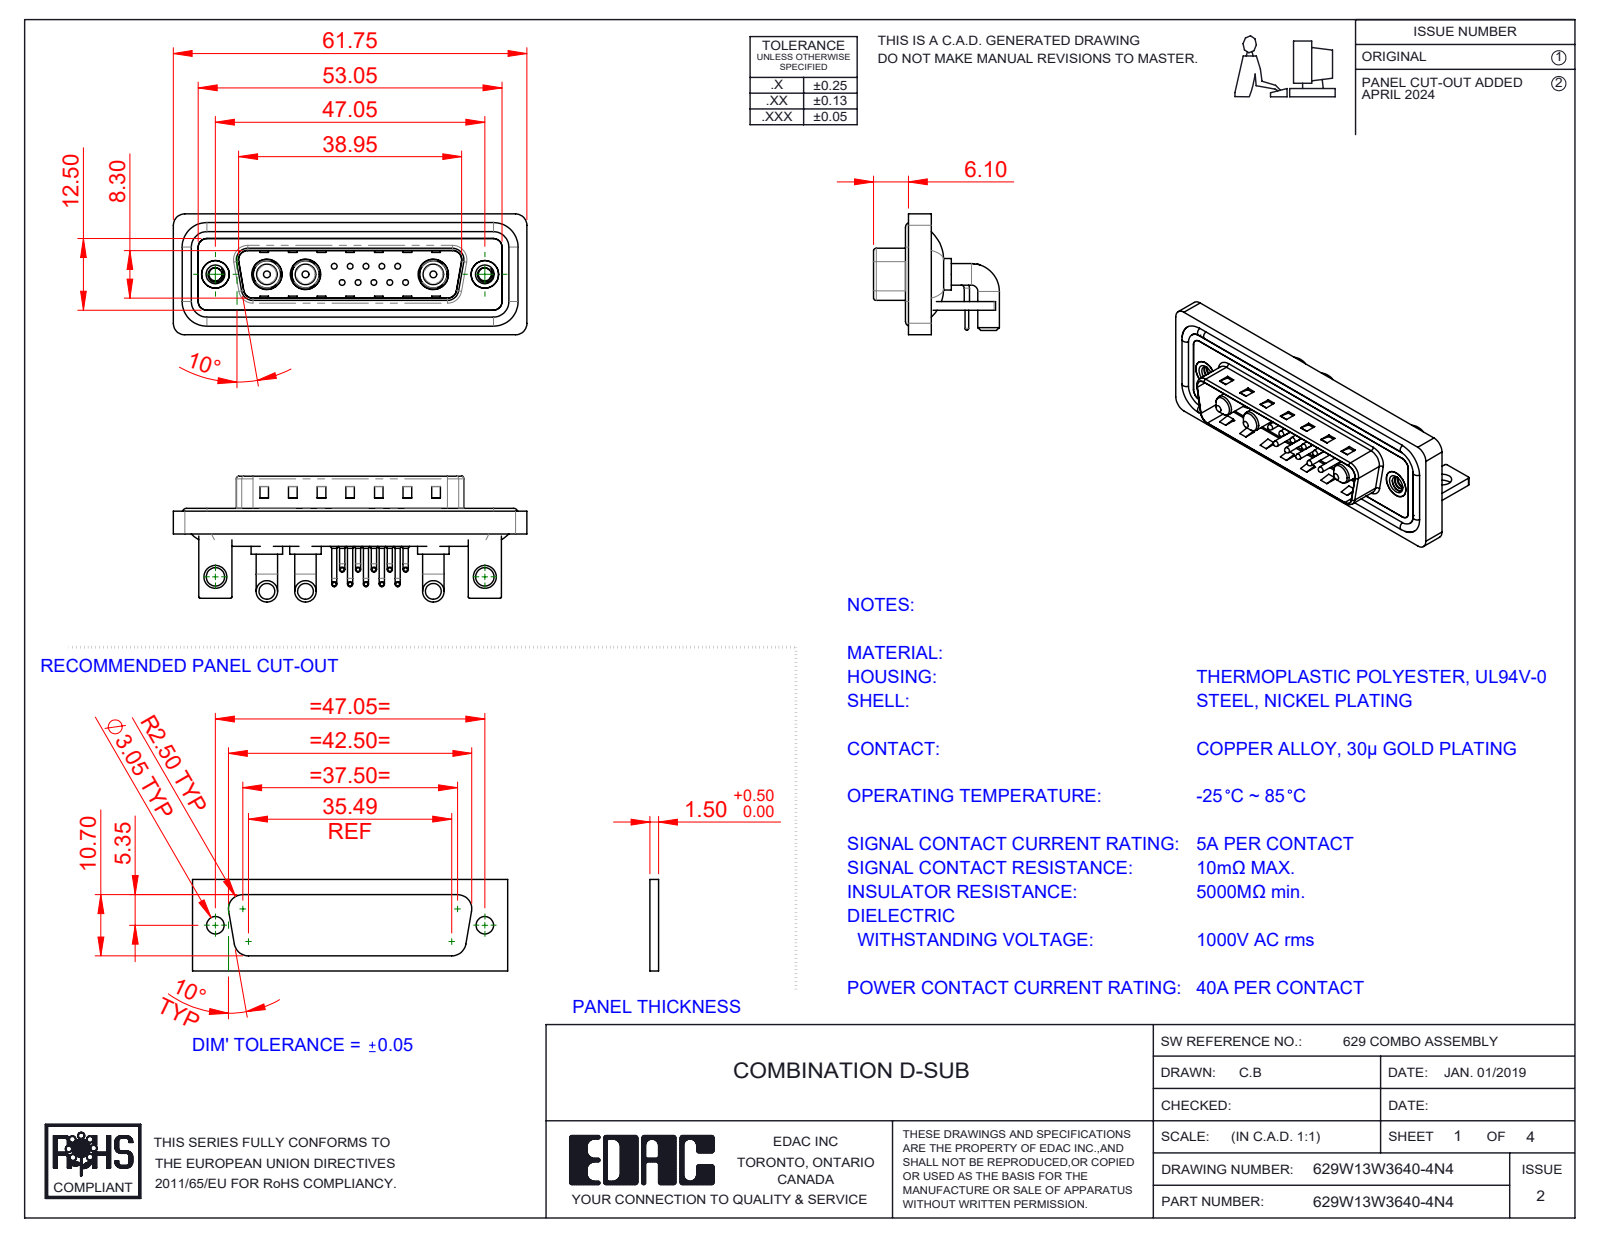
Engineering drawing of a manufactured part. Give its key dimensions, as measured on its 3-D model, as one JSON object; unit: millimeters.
{"part_name": "Power Pin_40A RA; 629Combo Waterproof Housing_25 Contacts; 629Combo Stabilizer Bracket; 629Combo Housing_13W3 (+6 more)", "step_written_by": "SolidWorks 2023 (CONFIG_CONTROL_DESIGN)", "units": "millimeters", "bodies": {"solids": 25, "faces": 1752, "planar": 899, "cylindrical": 629, "other": 224}, "overall_size": [61.75, 21.98, 21.1], "volume_mm3": 8106, "surface_area_mm2": 13215, "round_holes": [[0.75, 10], [1.6, 10], [2, 10], [4.85, 3], [5.3, 3], [2.26, 2], [3.2, 2], [4, 2], [4.8, 2], [5, 2]], "round_bosses_or_shafts": [[0.9, 20], [1.5, 10], [1, 10], [0.65, 10], [3.75, 6], [1.6, 4], [5.5, 3], [5.2, 3]], "partial_cylinders_radius": [[2, 19], [1.5, 18], [0.25, 16], [1.01, 10], [0.5, 9], [1.6, 8], [0.6, 4], [0.65, 4]], "face_to_face_distances": [0.4, 0.8, 1.5, 2.9, 2.1, 1.1, 4.1, 1.6, 3.7, 4.5], "hole_center_spacings": [3.16, 2.77, 5.04, 5.54, 7.49, 5.03, 8.31, 10.11]}
